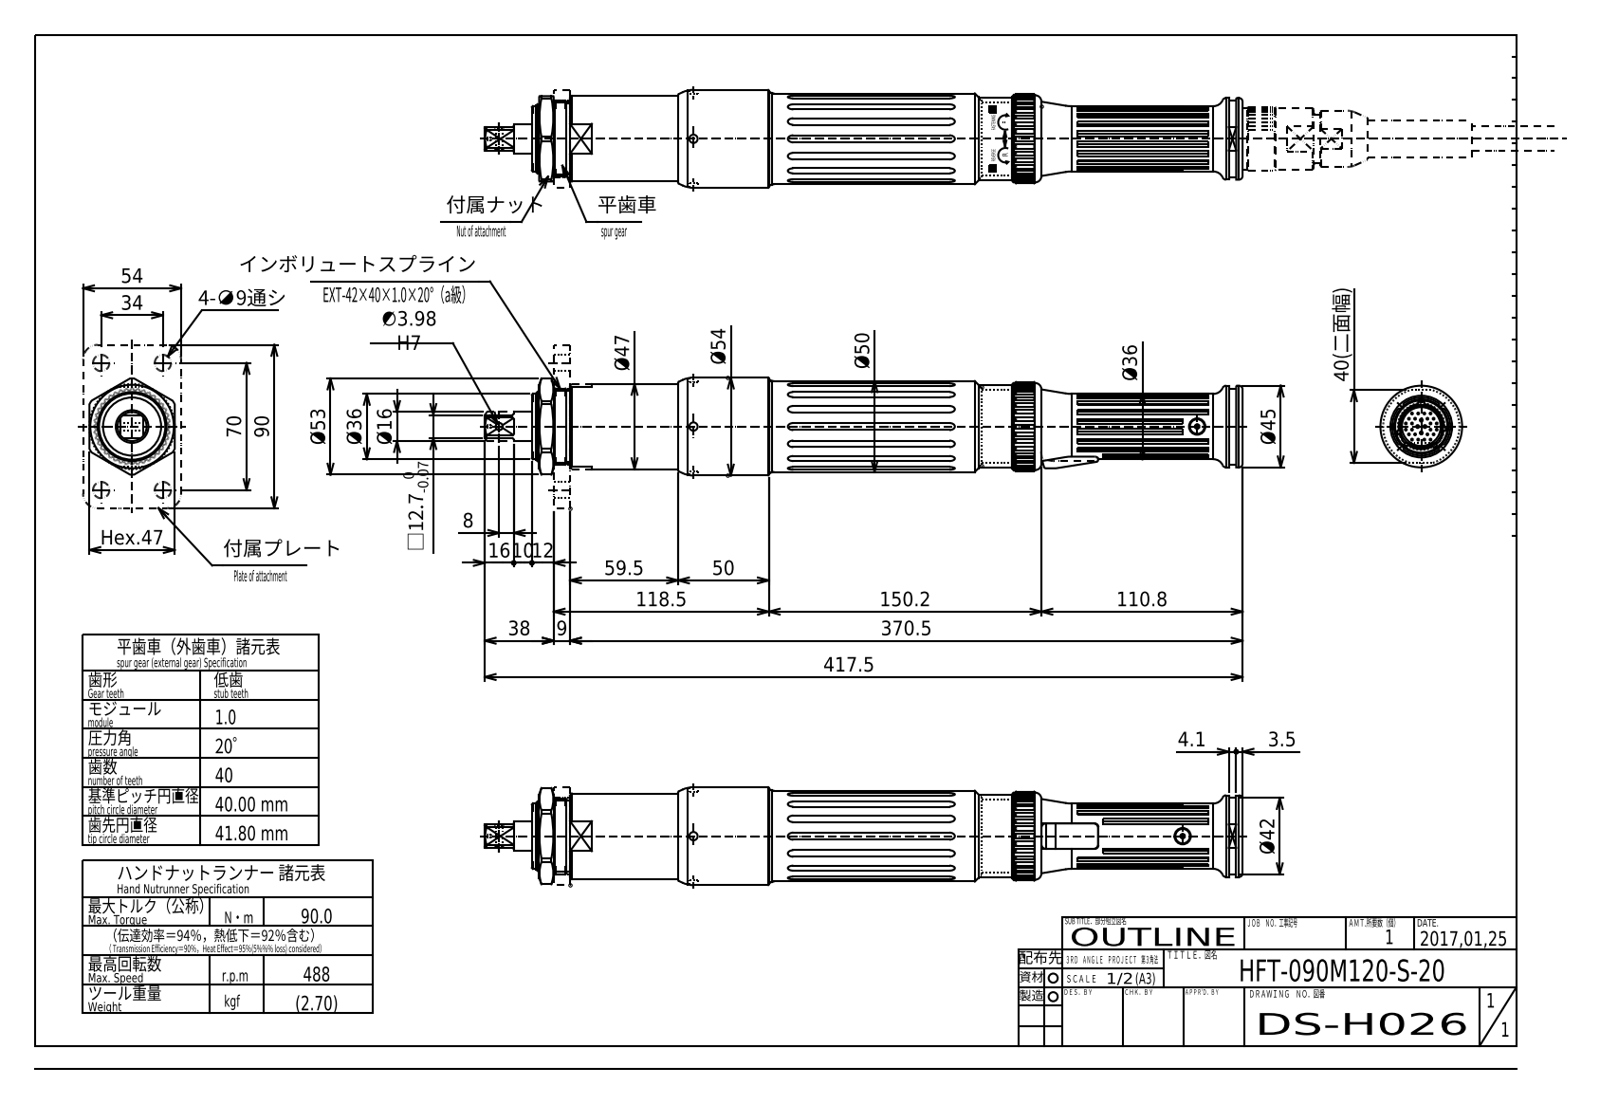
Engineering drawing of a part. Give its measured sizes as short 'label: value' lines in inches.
name: HFT-090M120-A-20(DS-H025)_OUTLINE
written by: Autodesk Inventor 2017 (AUTOMOTIVE_DESIGN)
unit: in
bodies: 1 solid, 836 faces (446 planar, 264 cylindrical, 126 other)
size: 16.437 × 3.543 × 2.126
volume: 40.96 in³; area: 124.3 in²
holes: 6× ⌀0.354, 2× ⌀0.181, 1× ⌀0.118, 1× ⌀0.157, 1× ⌀0.177, 1× ⌀0.236, 1× ⌀0.268, 1× ⌀0.89, 1× ⌀0.984, 1× ⌀1.016, 1× ⌀1.051, 1× ⌀1.339
bosses: 24× ⌀0.039, 4× ⌀0.063, 2× ⌀0.315, 2× ⌀0.157, 1× ⌀2.126, 1× ⌀2.047, 1× ⌀1.969, 1× ⌀1.89
rounds: 36× R0.004, 36× R0.059, 20× R0.118, 18× R0.013, 6× R0.039, 6× R0.098, 5× R0.012, 4× R0.315
face distances: 0.354, 1.376, 1.85, 2.126, 0.709, 15.295, 0.039, 14.65, 0.315, 0.669
hole spacings: 1.532, 1.339, 2.756, 3.064, 0.433, 2.311, 2.744, 4.213
